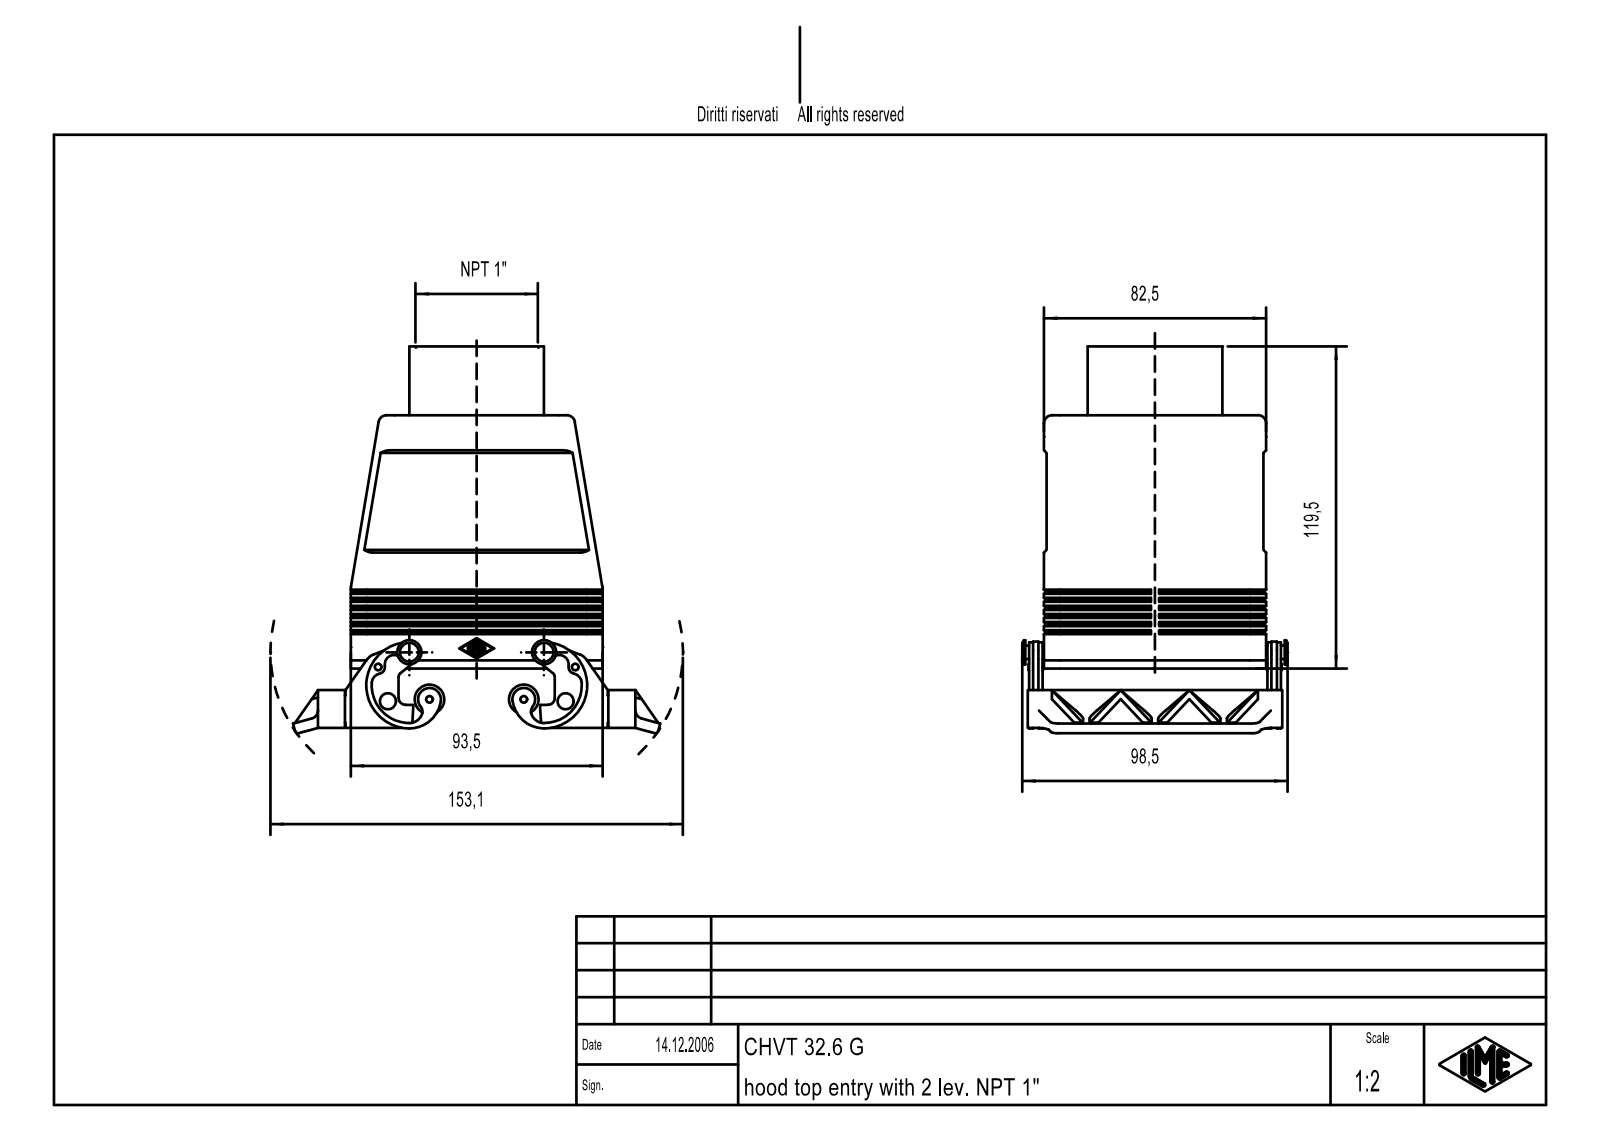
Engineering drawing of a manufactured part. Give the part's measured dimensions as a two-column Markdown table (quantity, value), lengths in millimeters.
| quantity | value |
| --- | --- |
| part name | CHV_32_G; CHV_32_G.stp |
| STEP written by | Creo Elements/Direct Modeling 18.0B 02-Dec-2011 (C) Parametric Technology GmbH (AUTOMOTIVE_DESIGN) |
| units | millimeters |
| bodies | 1 solid, 934 faces (502 planar, 310 cylindrical, 122 other) |
| overall size | 143.53 × 136.28 × 98.5 |
| volume | 216 382 mm³ |
| surface area | 102 542 mm² |
| round holes (diameter × count) | 2.46 × 8, 3.5 × 8, 2.5 × 2, 6 × 2 |
| round bosses / shafts (diameter × count) | 11 × 2, 9 × 2, 5 × 2, 2 × 2, 65 × 1, 59 × 1, 50 × 1 |
| partial cylindrical surfaces (radius × count) | 0.25 × 14, 3 × 14, 6 × 14, 2 × 12, 1 × 6, 2.5 × 6, 3.5 × 4, 5 × 4 |
| main face-to-face distances | 4, 78.5, 3, 82.5, 74.5, 1, 81.5, 77.5, 2, 8 |
| hole center spacings | 27, 35, 77.5, 82.07, 85.04, 8, 13.21, 62 |
